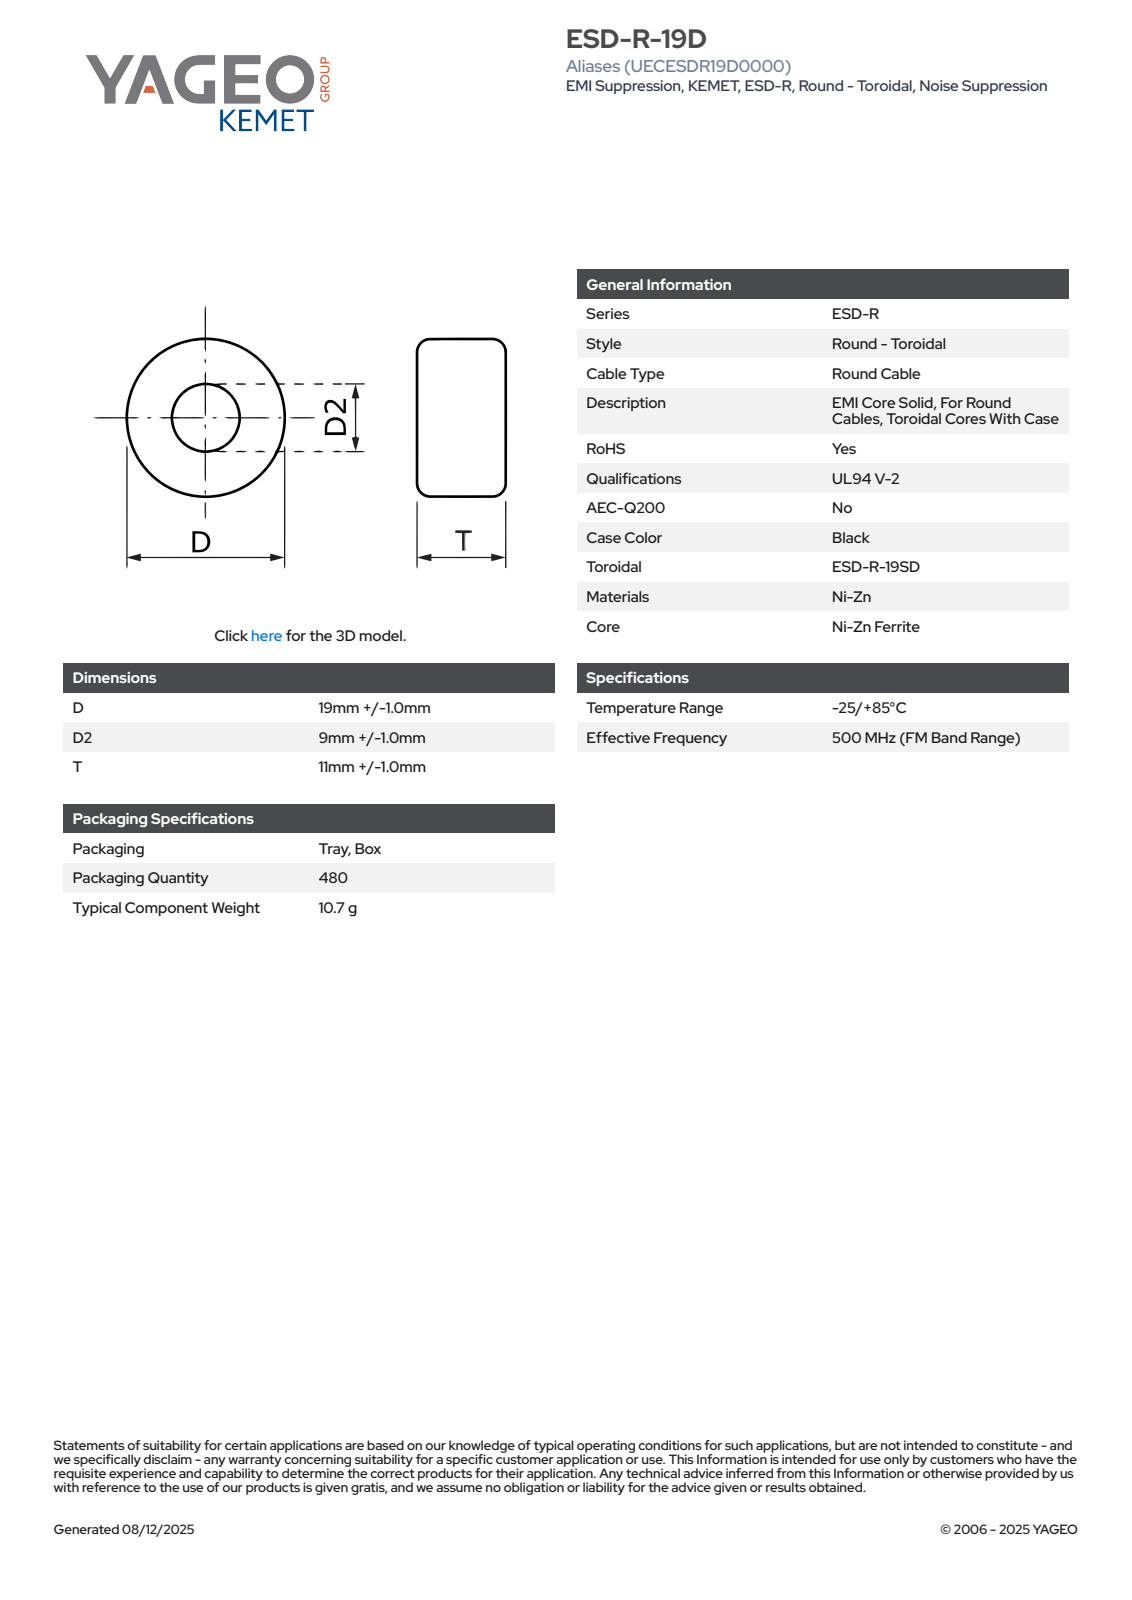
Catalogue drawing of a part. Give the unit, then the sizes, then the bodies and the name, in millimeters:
Units: millimetres
Overall size (bounding box): 20.01 × 20 × 12
Round holes (diameter × count): ⌀9 ×1
Round bosses / shafts (diameter × count): ⌀20 ×1
Partial cylindrical surfaces — rounded edges, fillets, slot ends (radius × count): R10.01 ×1
Main face-to-face distances: 12, 5.15, 6.85, 1.7, 0.32, 5.47, 6.53, 1.38, 1.06, 6.21
Volume: 2 996 mm³ · Surface area: 1 564 mm²
Bodies: 1 solid, 66 faces (24 planar, 7 cylindrical, 35 other)
Part name (STEP PRODUCT): EC_KBC_D20D29T12
STEP written by: SolidWorks 2021 (AUTOMOTIVE_DESIGN)
